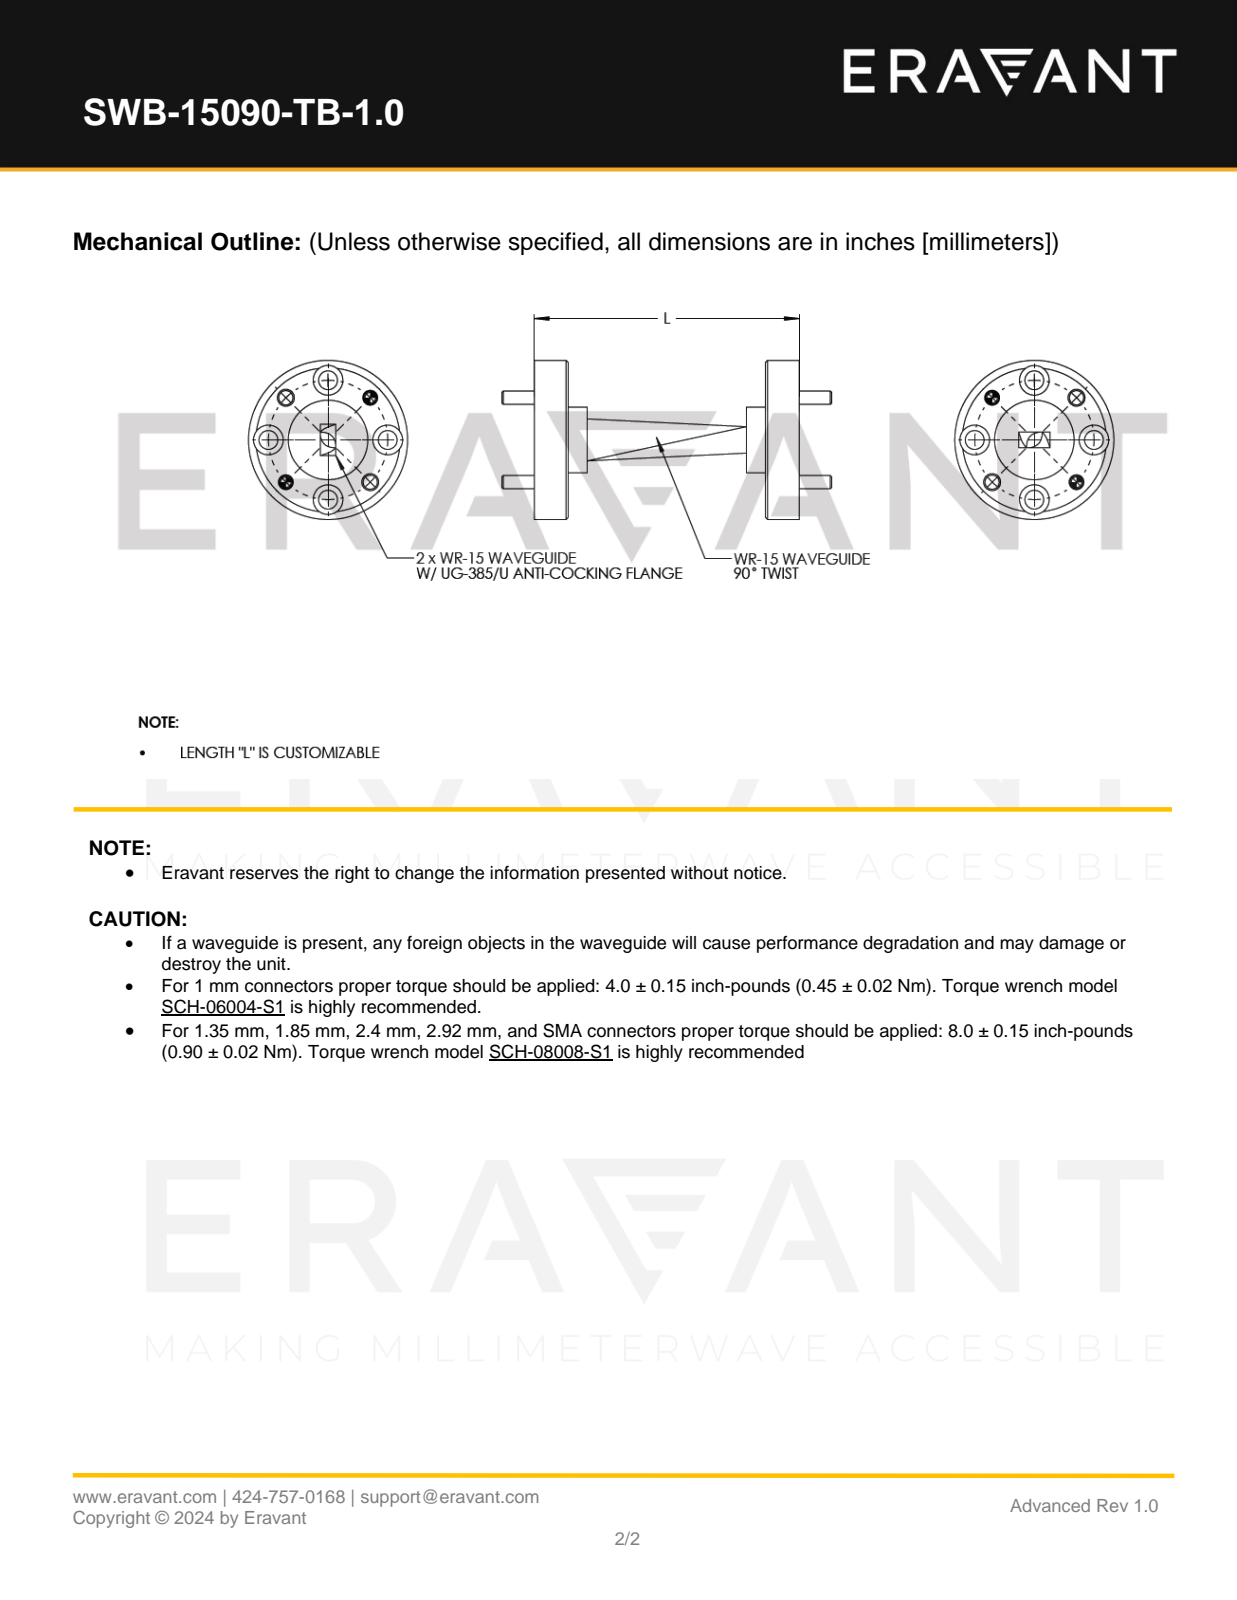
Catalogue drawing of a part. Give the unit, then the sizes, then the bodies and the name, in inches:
Units: inches
Overall size (bounding box): 1.305 × 0.75 × 0.75
Round holes (diameter × count): ⌀0.14 ×7, ⌀0.089 ×4, ⌀0.061 ×2, ⌀0.067 ×2, ⌀0.68 ×1
Round bosses / shafts (diameter × count): ⌀0.063 ×2, ⌀0.75 ×1, ⌀0.375 ×1, ⌀0.31 ×1
Main face-to-face distances: 0.14, 0.82, 0.68, 0.96, 0.98, 0.84, 0.16, 0.02, 0.02, 0.16
Hole centre spacings: 0.398, 0.215, 0.519, 0.281, 0.562, 0.52, 0.215, 0.281
Volume: 0.134 in³ · Surface area: 4.069 in²
Bodies: 5 solids, 158 faces (34 planar, 76 cylindrical, 48 other)
Part name (STEP PRODUCT): WB-TV-A-L, Defeatured
STEP written by: SolidWorks 2021 (AUTOMOTIVE_DESIGN)
